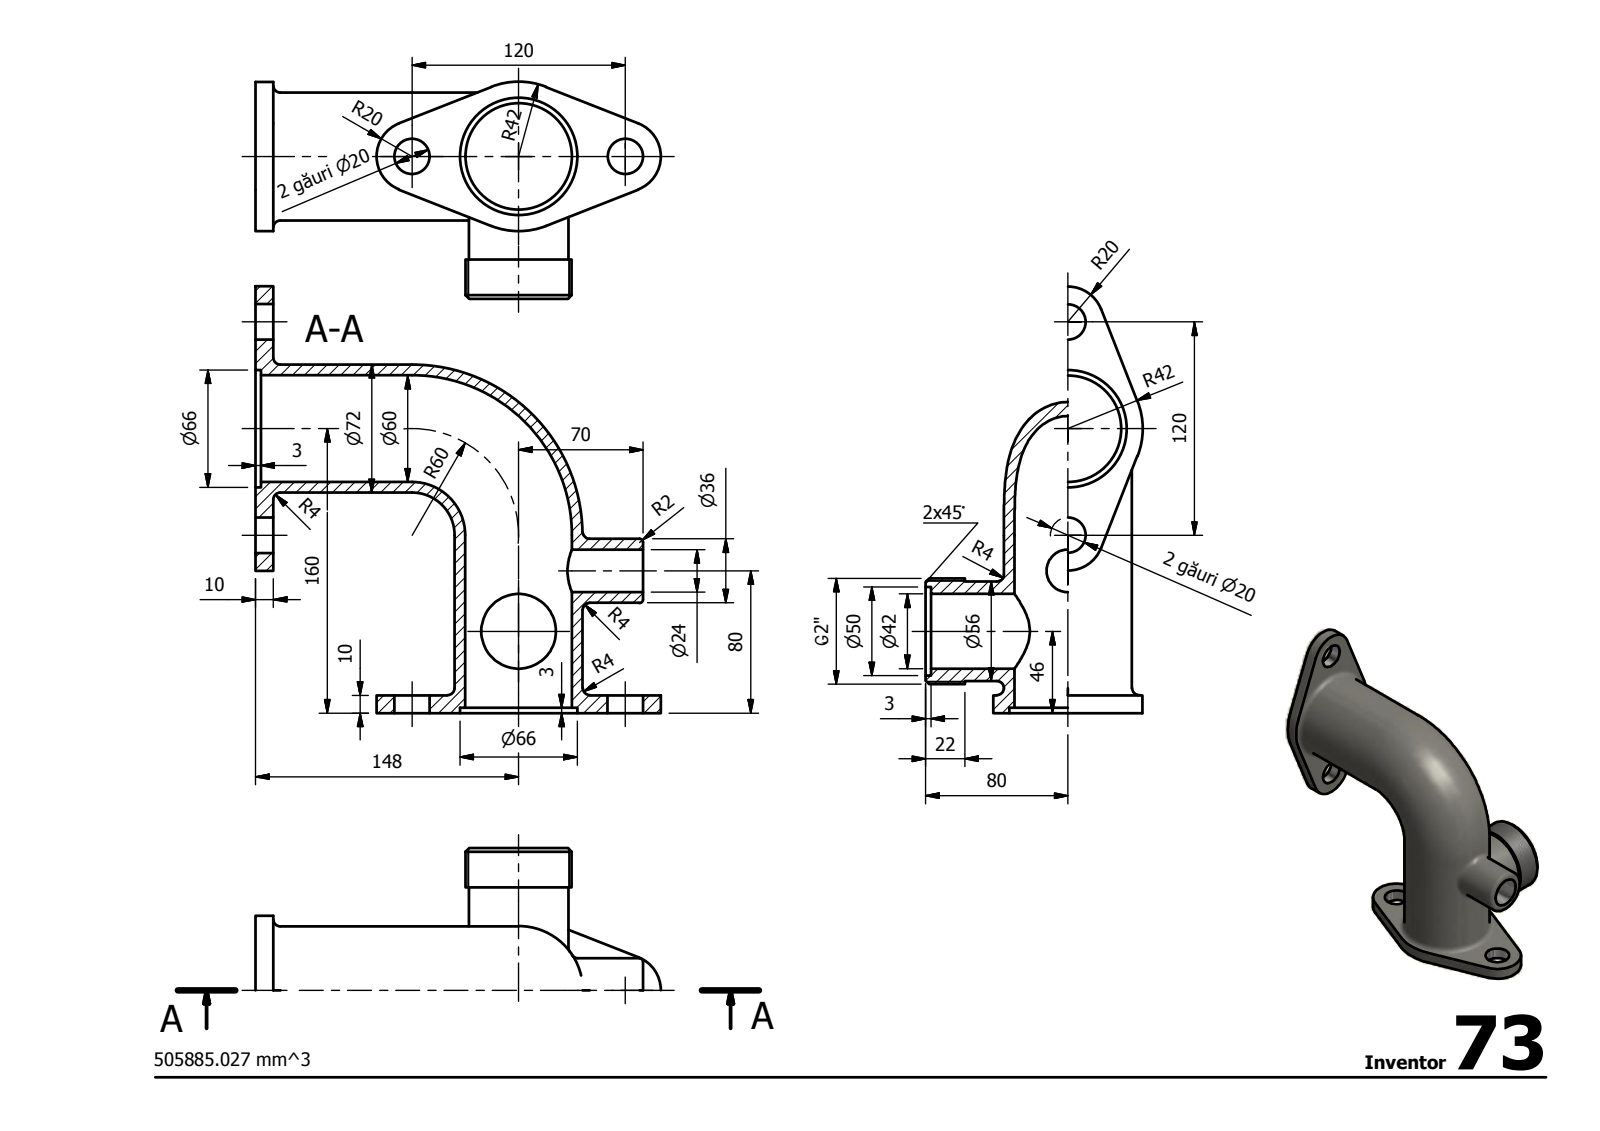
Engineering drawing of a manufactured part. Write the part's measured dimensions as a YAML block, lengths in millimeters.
step_written_by: "Autodesk Inventor 2014 (AUTOMOTIVE_DESIGN)"
units: millimeters
bodies: {solids: 1, faces: 51, planar: 18, cylindrical: 24, other: 9}
overall_size: [240, 228, 122]
volume: 505916
surface_area: 162080
round_holes:
  - {diameter: 20, count: 4}
  - {diameter: 60, count: 2}
  - {diameter: 66, count: 2}
  - {diameter: 24, count: 1}
  - {diameter: 42, count: 1}
  - {diameter: 50, count: 1}
round_bosses_or_shafts:
  - {diameter: 72, count: 2}
  - {diameter: 59.61, count: 1}
  - {diameter: 56, count: 1}
  - {diameter: 36, count: 1}
partial_cylinders:
  - {radius: 20, count: 4}
  - {radius: 42, count: 2}
face_to_face_distances: [10, 3, 7, 84.04, 83.98, 218, 215, 208, 19, 22]
hole_center_spacings: [60, 120, 20, 80, 140]
